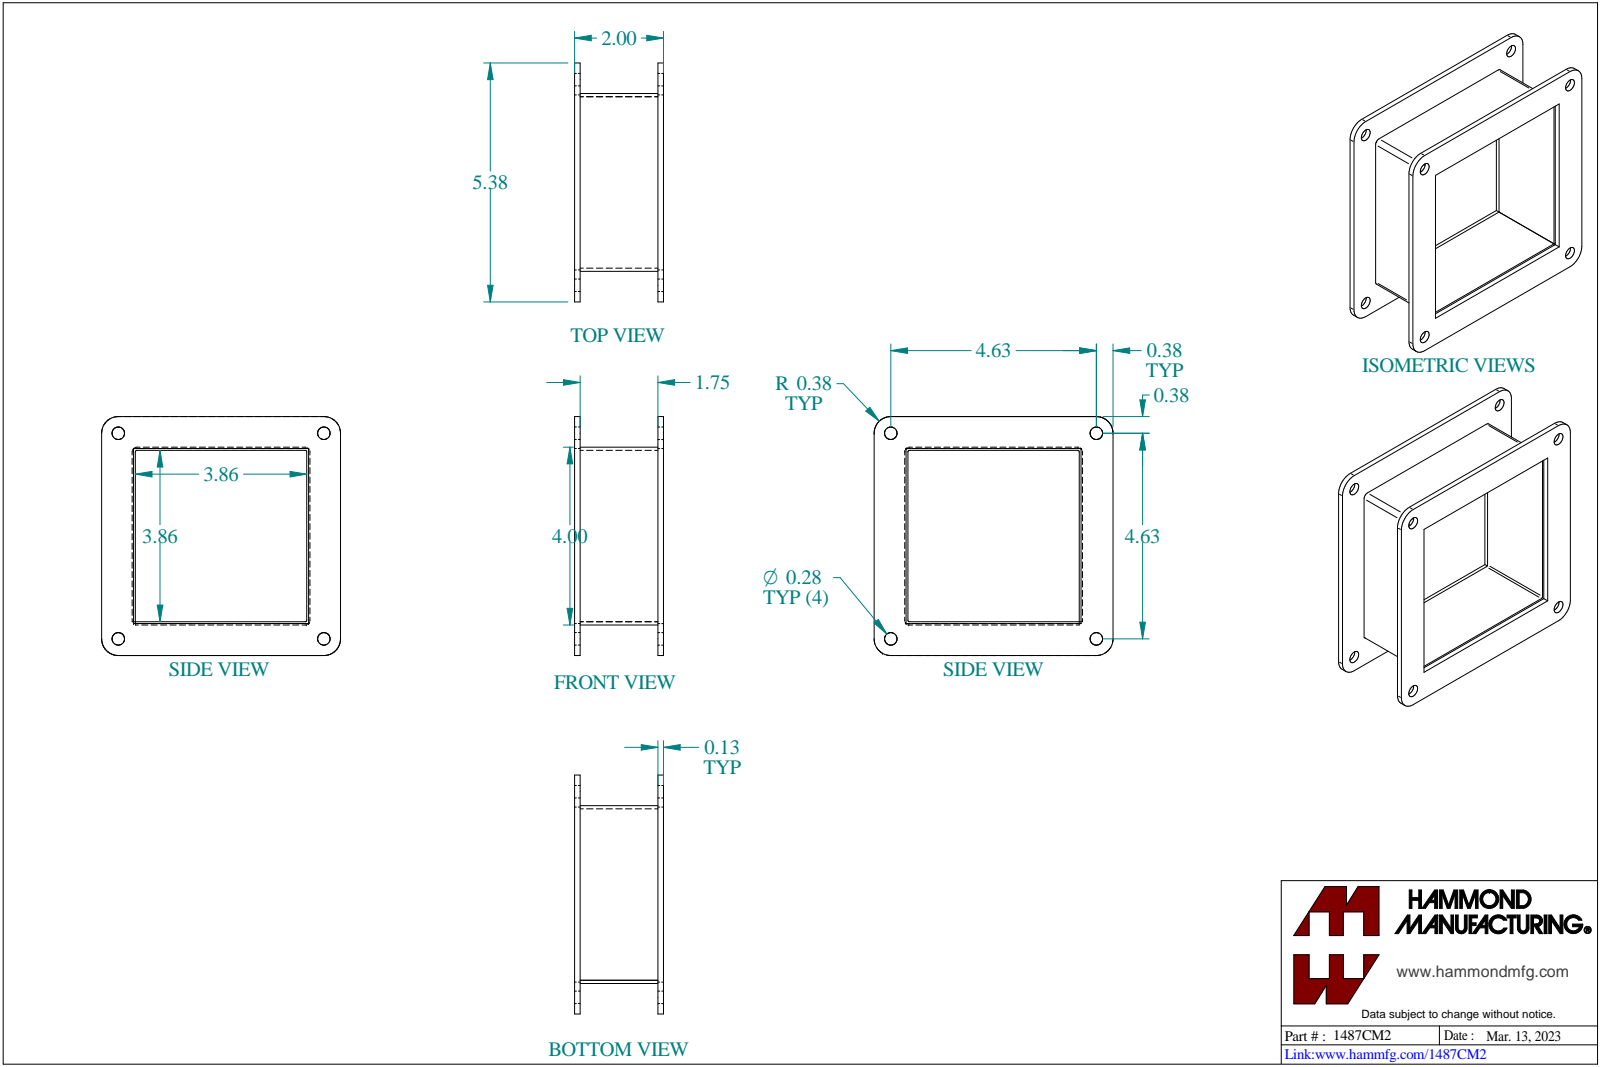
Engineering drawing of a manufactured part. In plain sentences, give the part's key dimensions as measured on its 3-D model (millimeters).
The part is named "1487CM2". Its 3-D file was written by "SolidWorks 2023 (CONFIG_CONTROL_DESIGN)". It is 4 solids with 96 faces: 42 planar, 54 cylindrical and 0 other. Overall it measures 136.6 by 136.5 by 54 millimeters. Its volume is 111 700 cubic millimeters and its surface area 96 770 square millimeters. Round holes: 12 of diameter 7.1. Partial cylindrical surfaces (rounded edges, fillets, slot ends): 8 of radius 9.5, 4 of radius 6.4, 3 of radius 0.9, 3 of radius 2.7. The main face-to-face distances are 3.2, 1.8, 99.8, 47.6, 50.8, 101.6, 97.9, 44.5, 54, 6.4. The hole center spacings are 117.5, 58.7, 58.8, 131.3, 131.3, 166.1, 83.1, 58.7.
